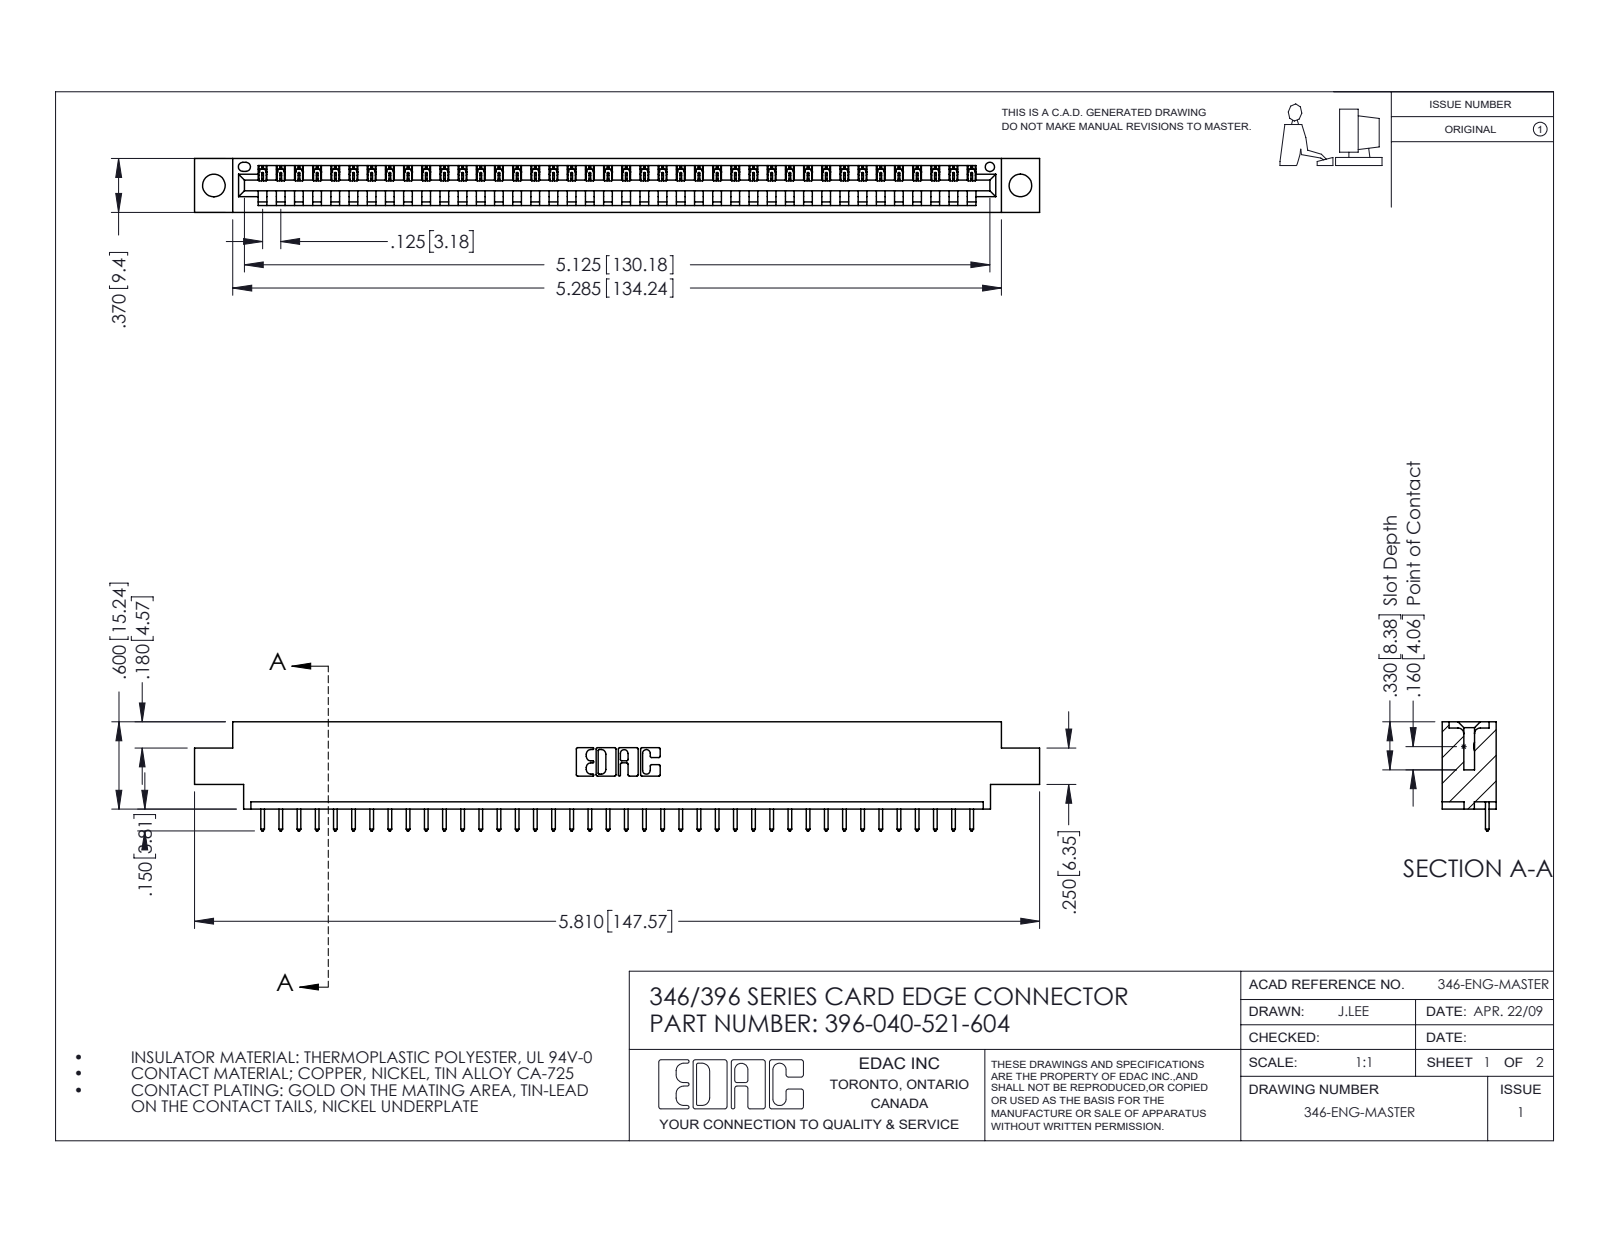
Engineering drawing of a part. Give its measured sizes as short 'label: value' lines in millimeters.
name: 346 Part_0.170 Offset - 0.156 Dia-TH; 345-292-001_345-293-121; 396-040-521-604
written by: SolidWorks 2016 (CONFIG_CONTROL_DESIGN)
unit: mm
bodies: 41 solids, 2446 faces (1680 planar, 766 cylindrical, 0 other)
size: 147.6 × 19.1 × 9.4
volume: 13 700 mm³; area: 16 680 mm²
holes: 2× ⌀4, 1× ⌀1.6
rounds: 80× R0.2, 80× R0.3, 22× R0.3, 6× R0.2, 6× R0.8, 3× R0.7, 2× R0.8, 2× R1
face distances: 1.2, 8.2, 9.4, 6.4, 1.8, 7.6, 0.6, 3.8, 5.6, 2.5
hole spacings: 6.2, 135.5, 140.8
